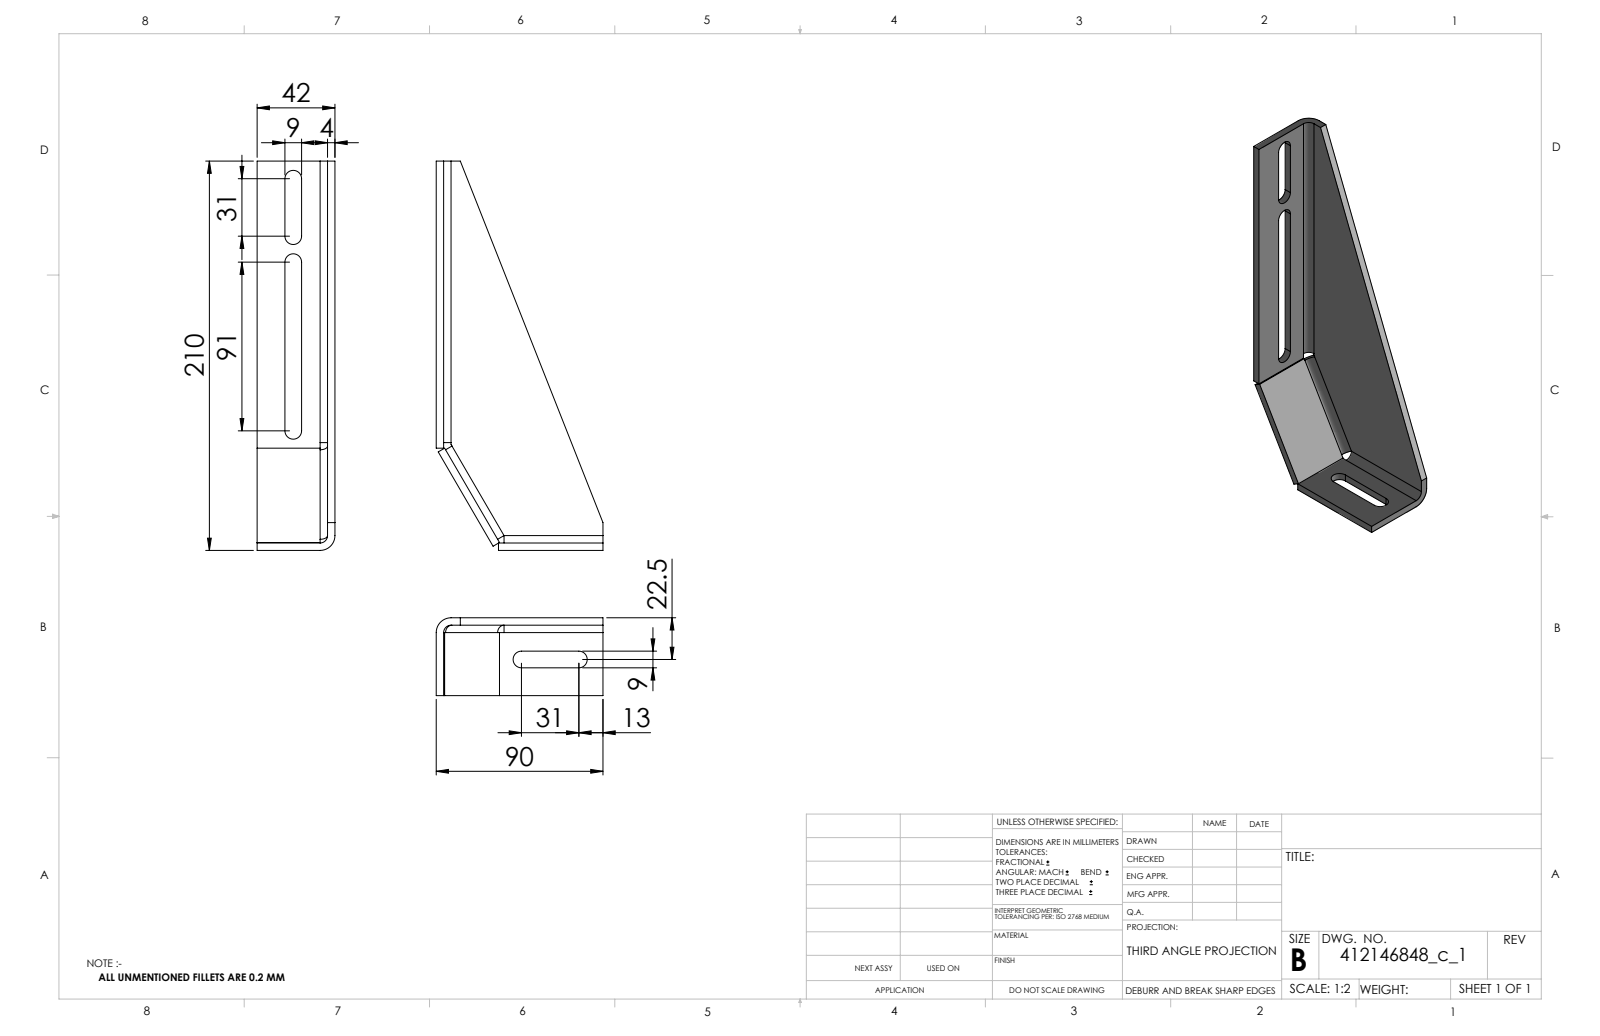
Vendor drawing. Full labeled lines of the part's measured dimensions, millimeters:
Part name (STEP PRODUCT): 412146848_c_1
STEP written by: SolidWorks 2014 (CONFIG_CONTROL_DESIGN)
Units: millimetres
Bodies: 1 solid, 49 faces (35 planar, 14 cylindrical, 0 other)
Overall size (bounding box): 210 × 90 × 42
Volume: 73 722 mm³ · Surface area: 41 470 mm²
Partial cylindrical surfaces — rounded edges, fillets, slot ends (radius × count): R4.5 ×6, R4 ×3, R8 ×3
Main face-to-face distances: 4, 38, 42, 15, 23, 27, 24, 9, 14, 18
